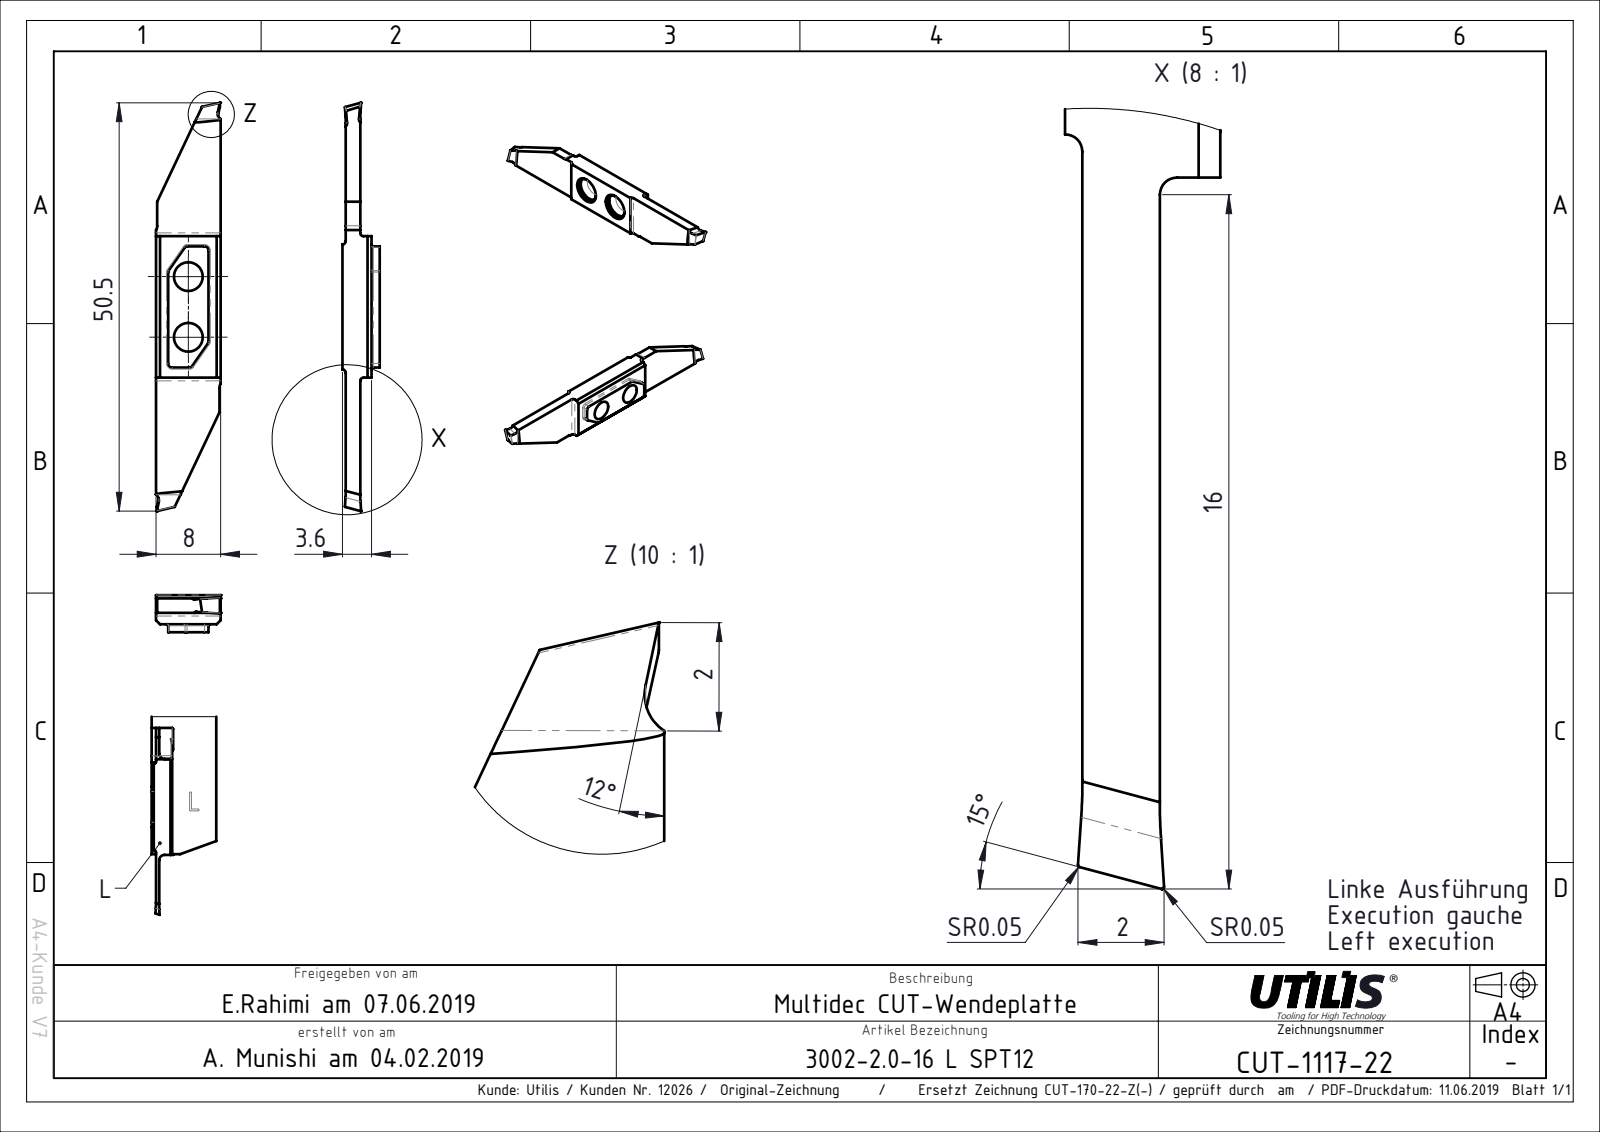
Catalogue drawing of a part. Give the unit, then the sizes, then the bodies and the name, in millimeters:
Units: millimetres
Overall size (bounding box): 50.5 × 8 × 3.6
Round holes (diameter × count): ⌀3.55 ×2
Partial cylindrical surfaces — rounded edges, fillets, slot ends (radius × count): R0.4 ×4, R1 ×2
Main face-to-face distances: 1.8, 0.4, 2.2, 3.6, 3.2, 1.4, 8, 18.09, 7.85, 17.5
Hole centre spacings: 7.5
Volume: 761 mm³ · Surface area: 964 mm²
Bodies: 1 solid, 40 faces (24 planar, 16 cylindrical, 0 other)
Part name (STEP PRODUCT): CUT-1117; ASME Y14.5
STEP written by: FormatWorks Professional (AP242_MANAGED_MODEL_BASED_3D_ENGINEERING_MIM_LF)
